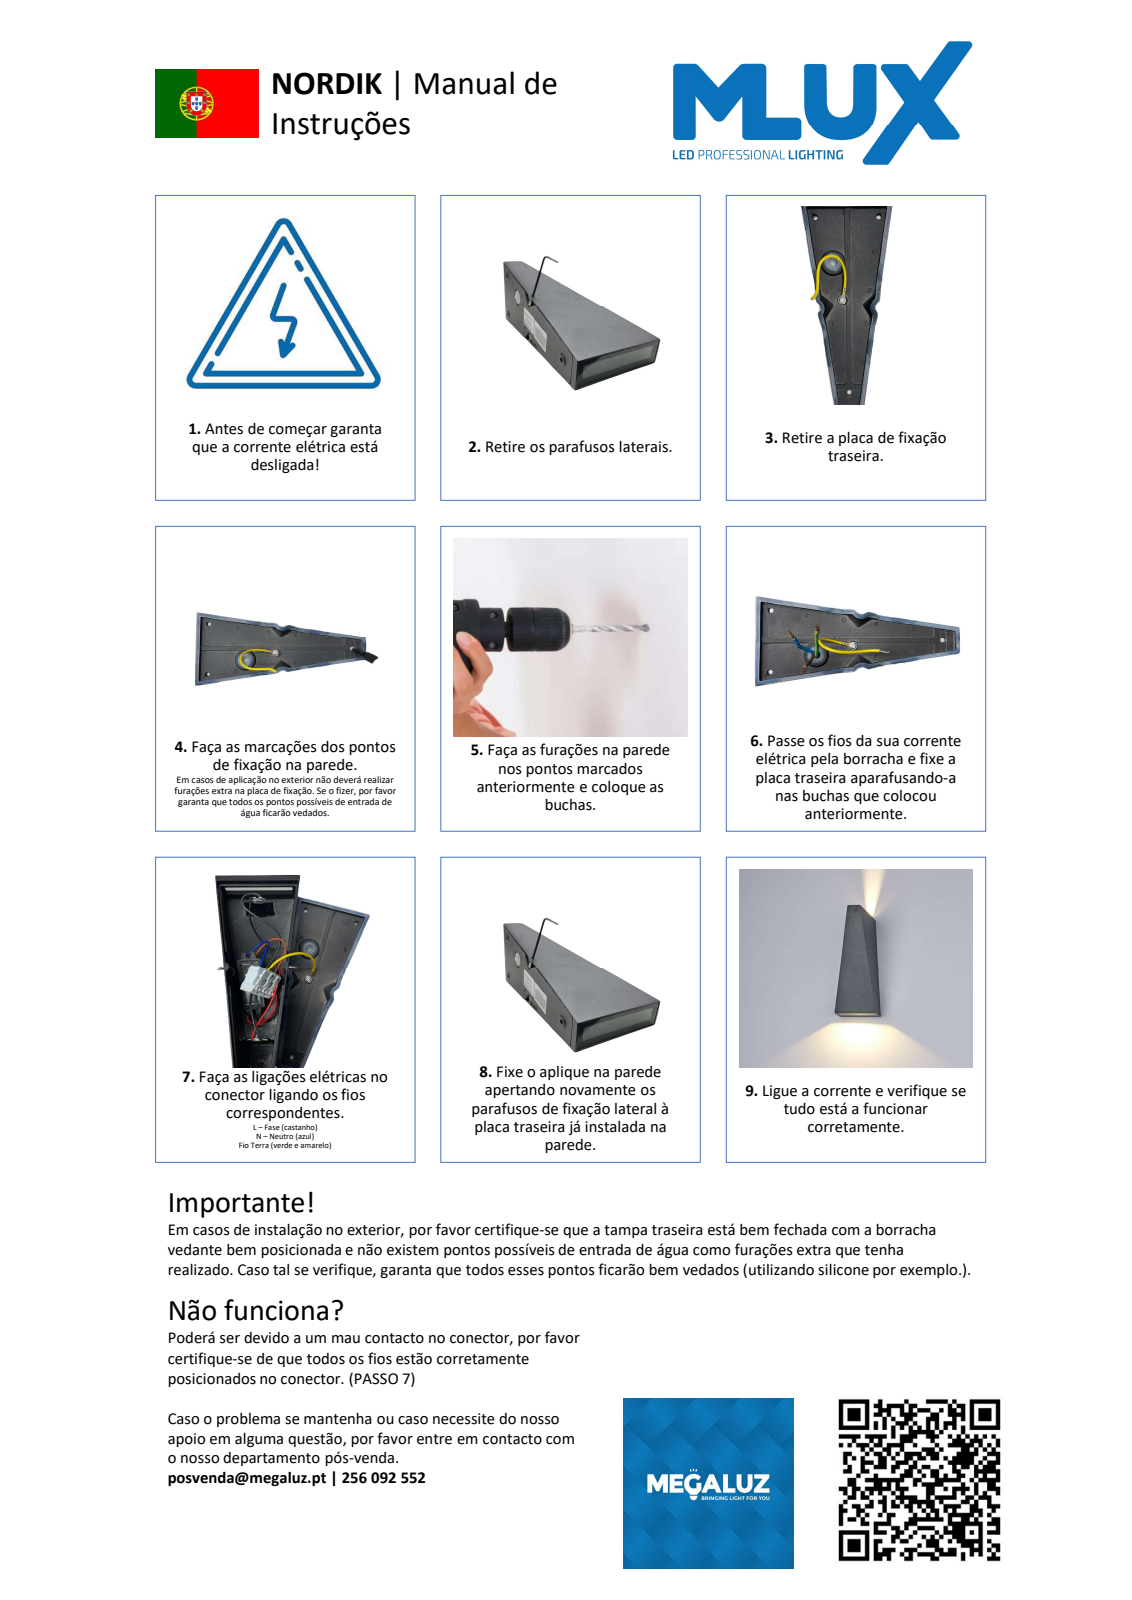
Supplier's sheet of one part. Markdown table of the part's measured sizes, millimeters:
| quantity | value |
| --- | --- |
| part name | BD-001-01; BD-001-02-S; BD-001-02-X; BD-001_ASM |
| STEP written by | CREO PARAMETRIC BY PTC INC, 2020053 (CONFIG_CONTROL_DESIGN) |
| units | millimeters |
| bodies | 3 solids, 70 faces (22 planar, 32 cylindrical, 16 other) |
| overall size | 205 × 84.92 × 84.91 |
| volume | 121 442 mm³ |
| surface area | 100 677 mm² |
| partial cylindrical surfaces (radius × count) | 0.3 × 16, 0.5 × 4, 3 × 4 |
| main face-to-face distances | 2.5, 2.51, 2, 197, 195, 199, 3, 5, 200, 202 |
